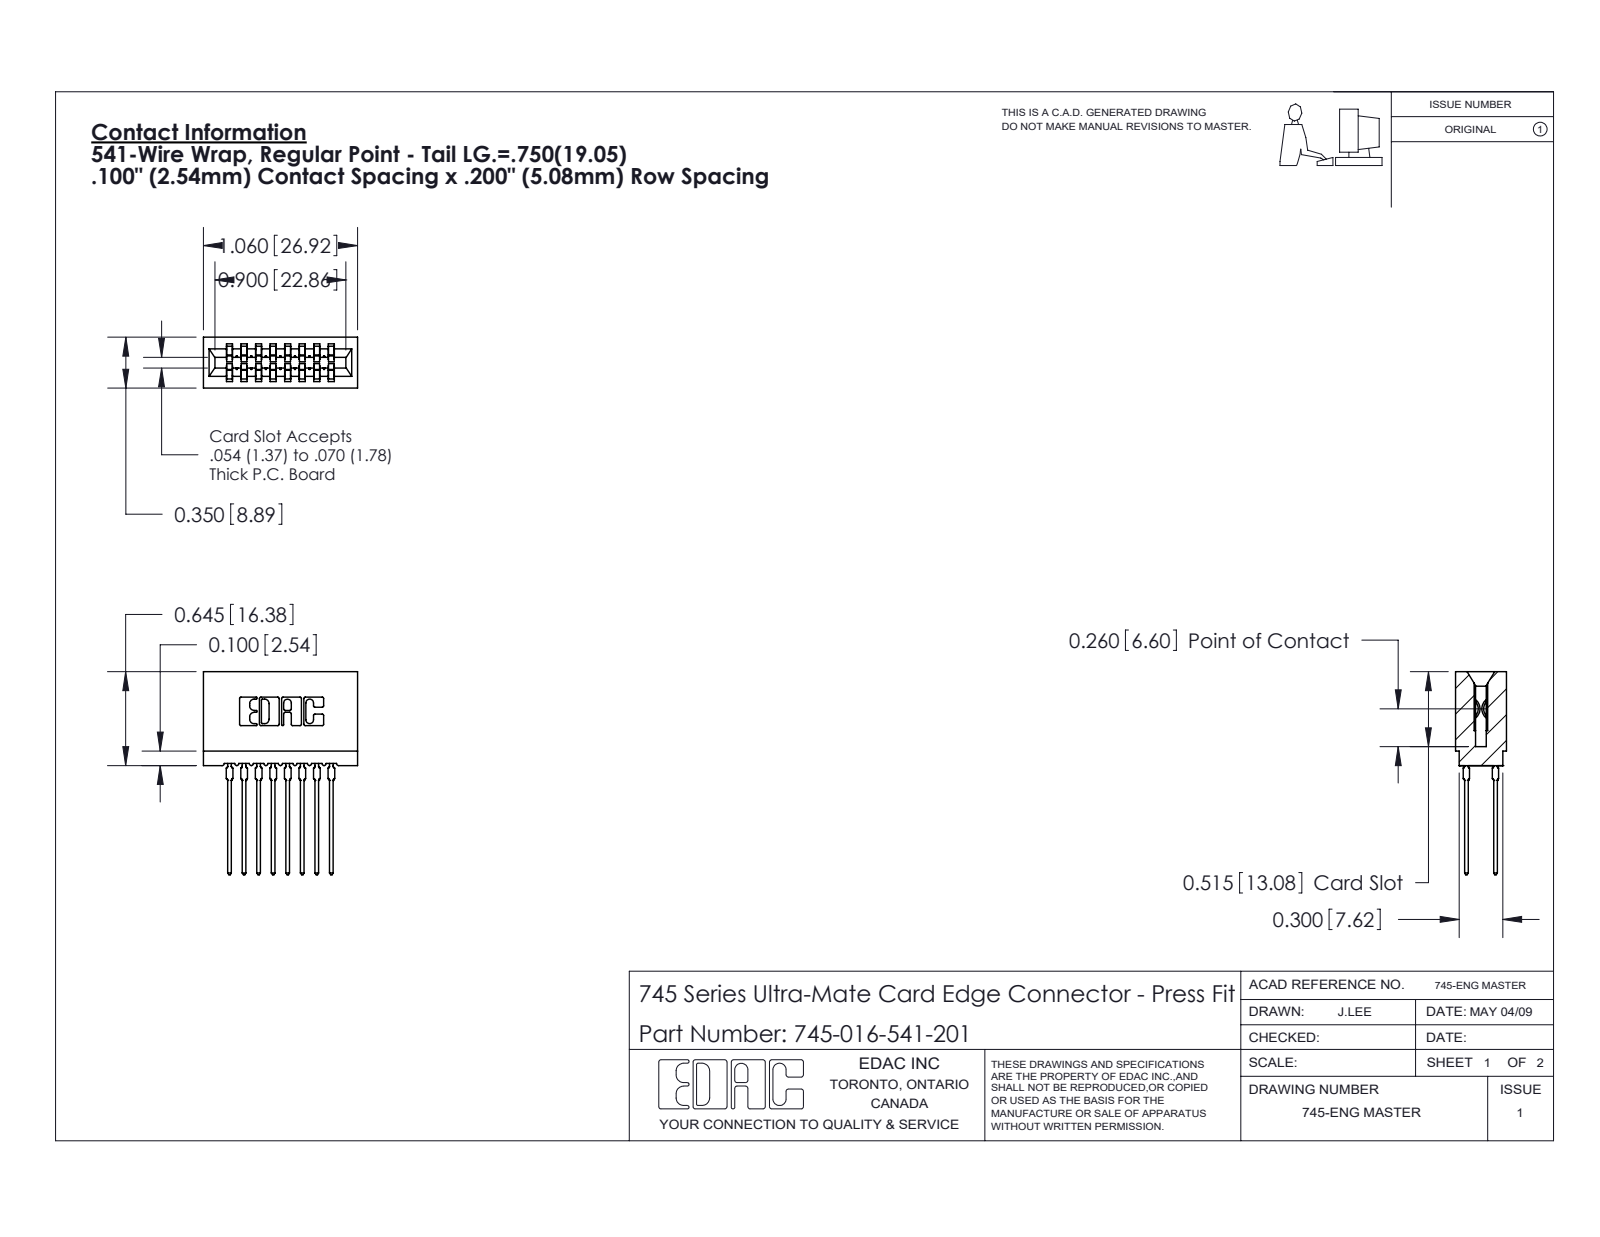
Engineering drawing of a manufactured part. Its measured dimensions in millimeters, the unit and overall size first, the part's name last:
Units: millimetres
Overall size (bounding box): 35.5 × 26.9 × 8.9
Partial cylindrical surfaces — rounded edges, fillets, slot ends (radius × count): R0.5 ×32, R0.3 ×22, R0.4 ×16, R0.1 ×8, R0.3 ×8, R0.2 ×6, R0.8 ×6, R0.7 ×3
Main face-to-face distances: 5.1, 2.5, 7.6, 1.1, 10.2, 3.6, 1.5, 6.1, 12.7, 4
Volume: 2 700 mm³ · Surface area: 5 037 mm²
Bodies: 17 solids, 1527 faces (791 planar, 320 cylindrical, 416 other)
Part name (STEP PRODUCT): 745-292-001_541; 745 Part_Insulator Option - 01; 745-016-541-201
STEP written by: SolidWorks 2020 (CONFIG_CONTROL_DESIGN)
